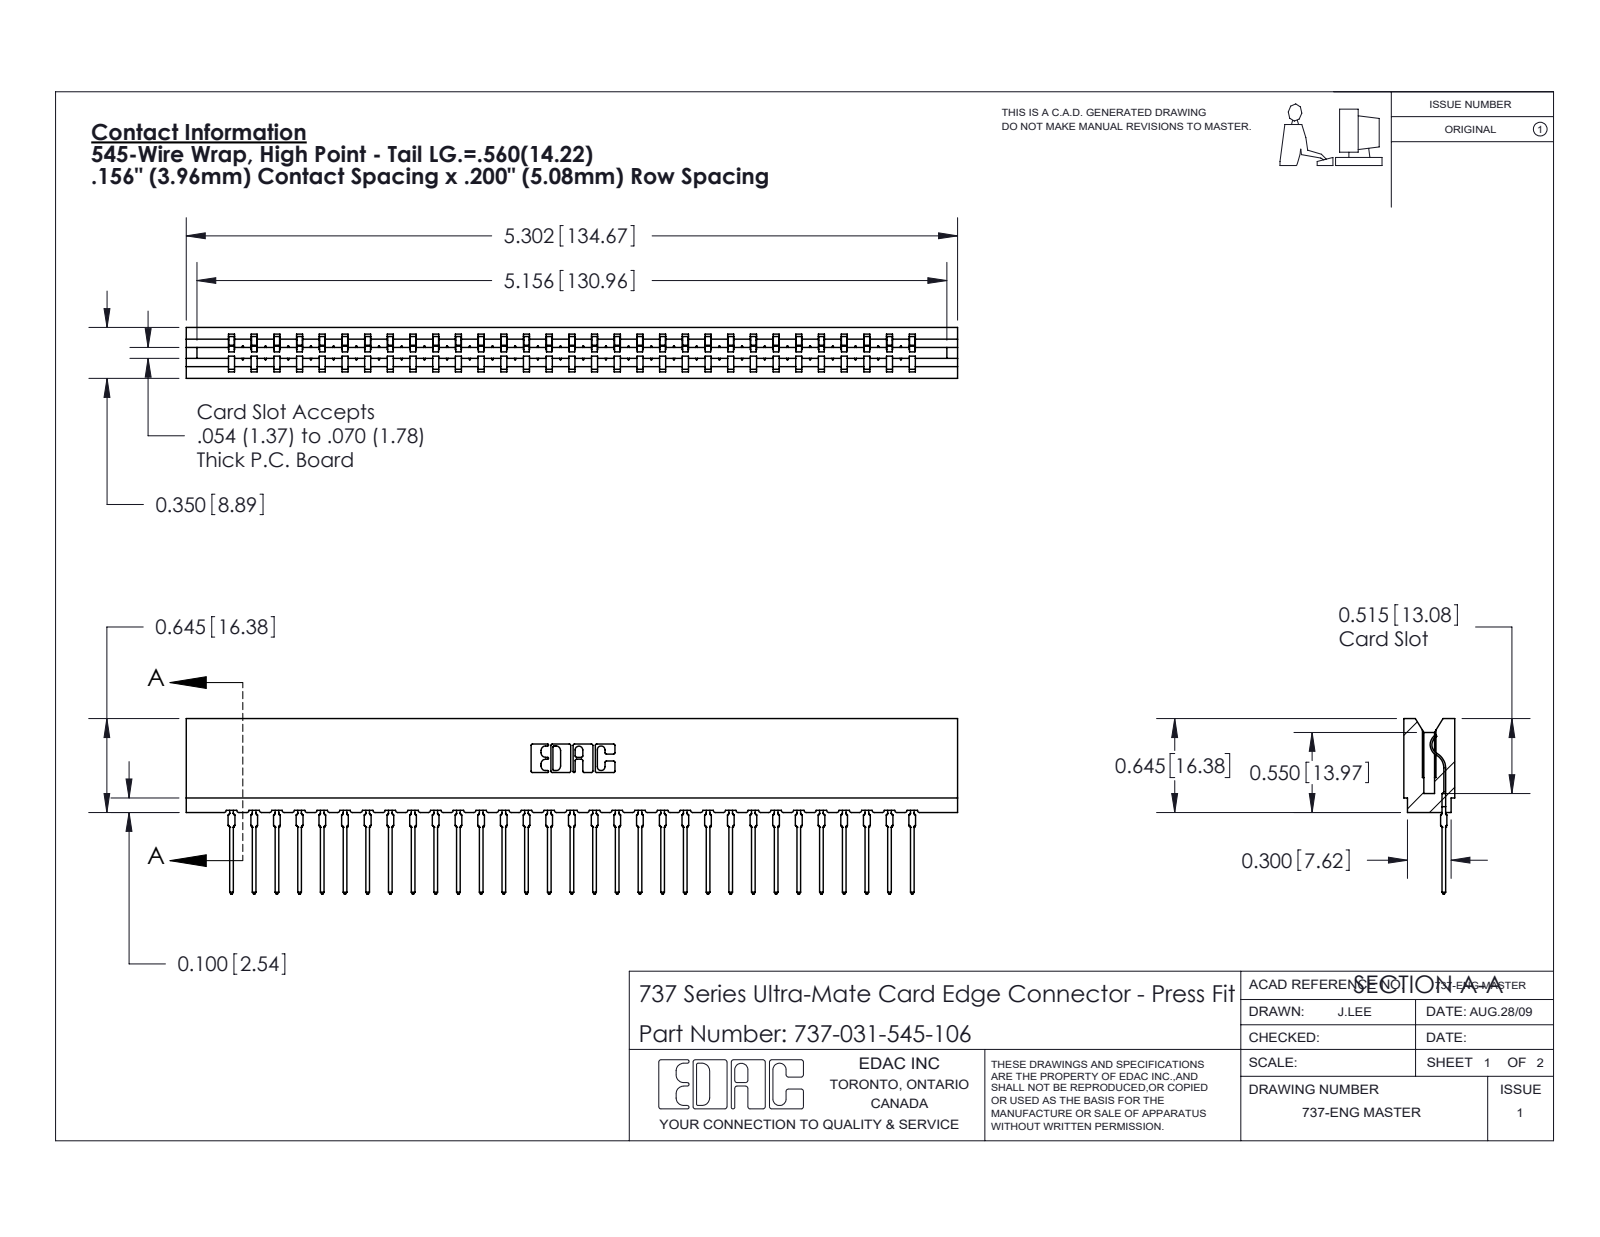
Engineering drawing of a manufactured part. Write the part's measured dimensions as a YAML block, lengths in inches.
part_name: "737-031-545-106; 737 Part_Insulator Option - 06; 745-292-001_545"
step_written_by: "SolidWorks 2020 (CONFIG_CONTROL_DESIGN)"
units: inches
bodies: {solids: 32, faces: 3598, planar: 2163, cylindrical: 629, other: 806}
overall_size: [5.302, 1.206, 0.35]
volume: 0.803
surface_area: 27.89
partial_cylinders:
  - {radius: 0.015, count: 62}
  - {radius: 0.021, count: 62}
  - {radius: 0.01, count: 22}
  - {radius: 0.007, count: 6}
  - {radius: 0.031, count: 6}
  - {radius: 0.005, count: 4}
  - {radius: 0.011, count: 4}
  - {radius: 0.026, count: 3}
face_to_face_distances: [0.138, 0.212, 0.35, 0.074, 0.045, 0.305, 0.093, 0.167, 0.063, 0.287]
